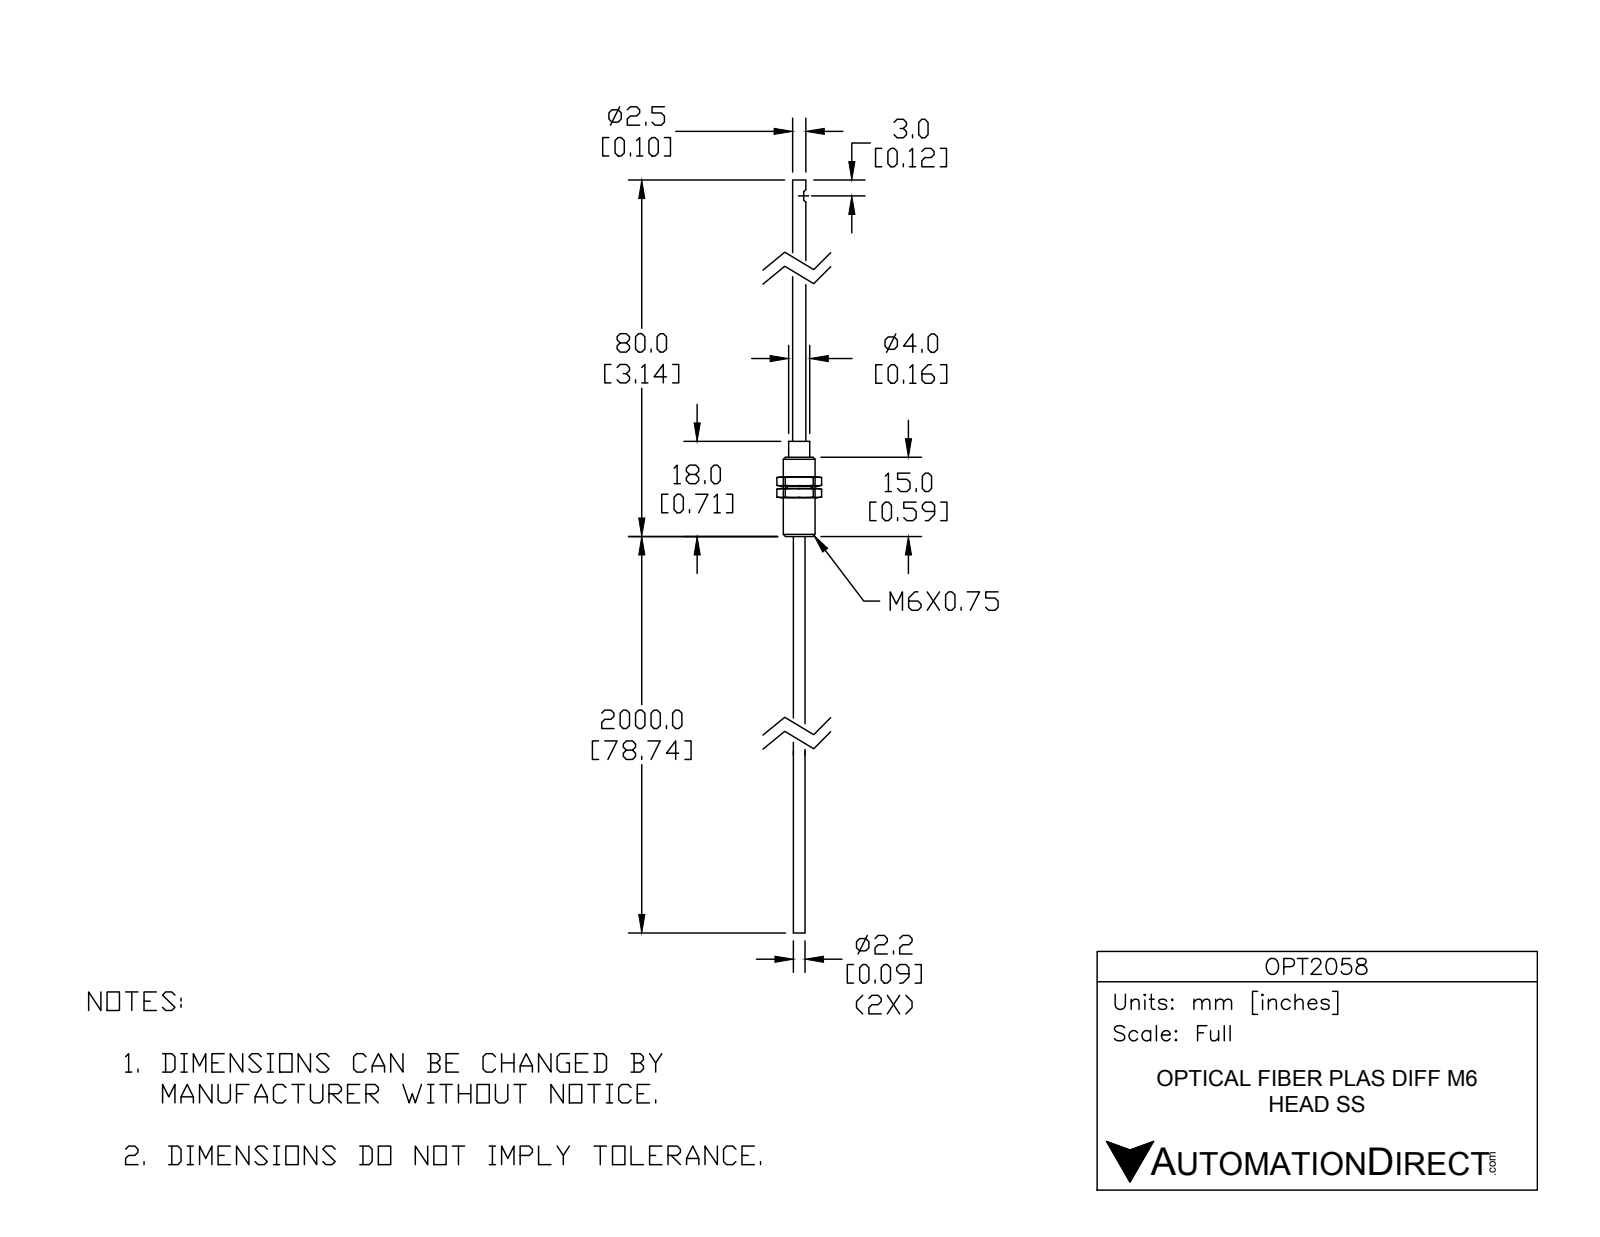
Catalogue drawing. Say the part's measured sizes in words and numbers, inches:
The part is named "OPT2058". Its 3-D file was written by "SolidWorks 2014 (AUTOMOTIVE_DESIGN)". It is 2 solids with 32 faces: 10 planar, 18 cylindrical and 4 other. Overall it measures 6.102 by 0.236 by 0.236 inches. Its volume is 0.078 cubic inches and its surface area 2.744 square inches. Round bosses or shafts: 2 of diameter 0.087, 1 of diameter 0.236, 1 of diameter 0.157, 1 of diameter 0.098. The main face-to-face distances are 0.591, 0.259, 0.118, 0.709, 3.661, 3.543, 2.953, 2.441, 2.559, 3.15.
